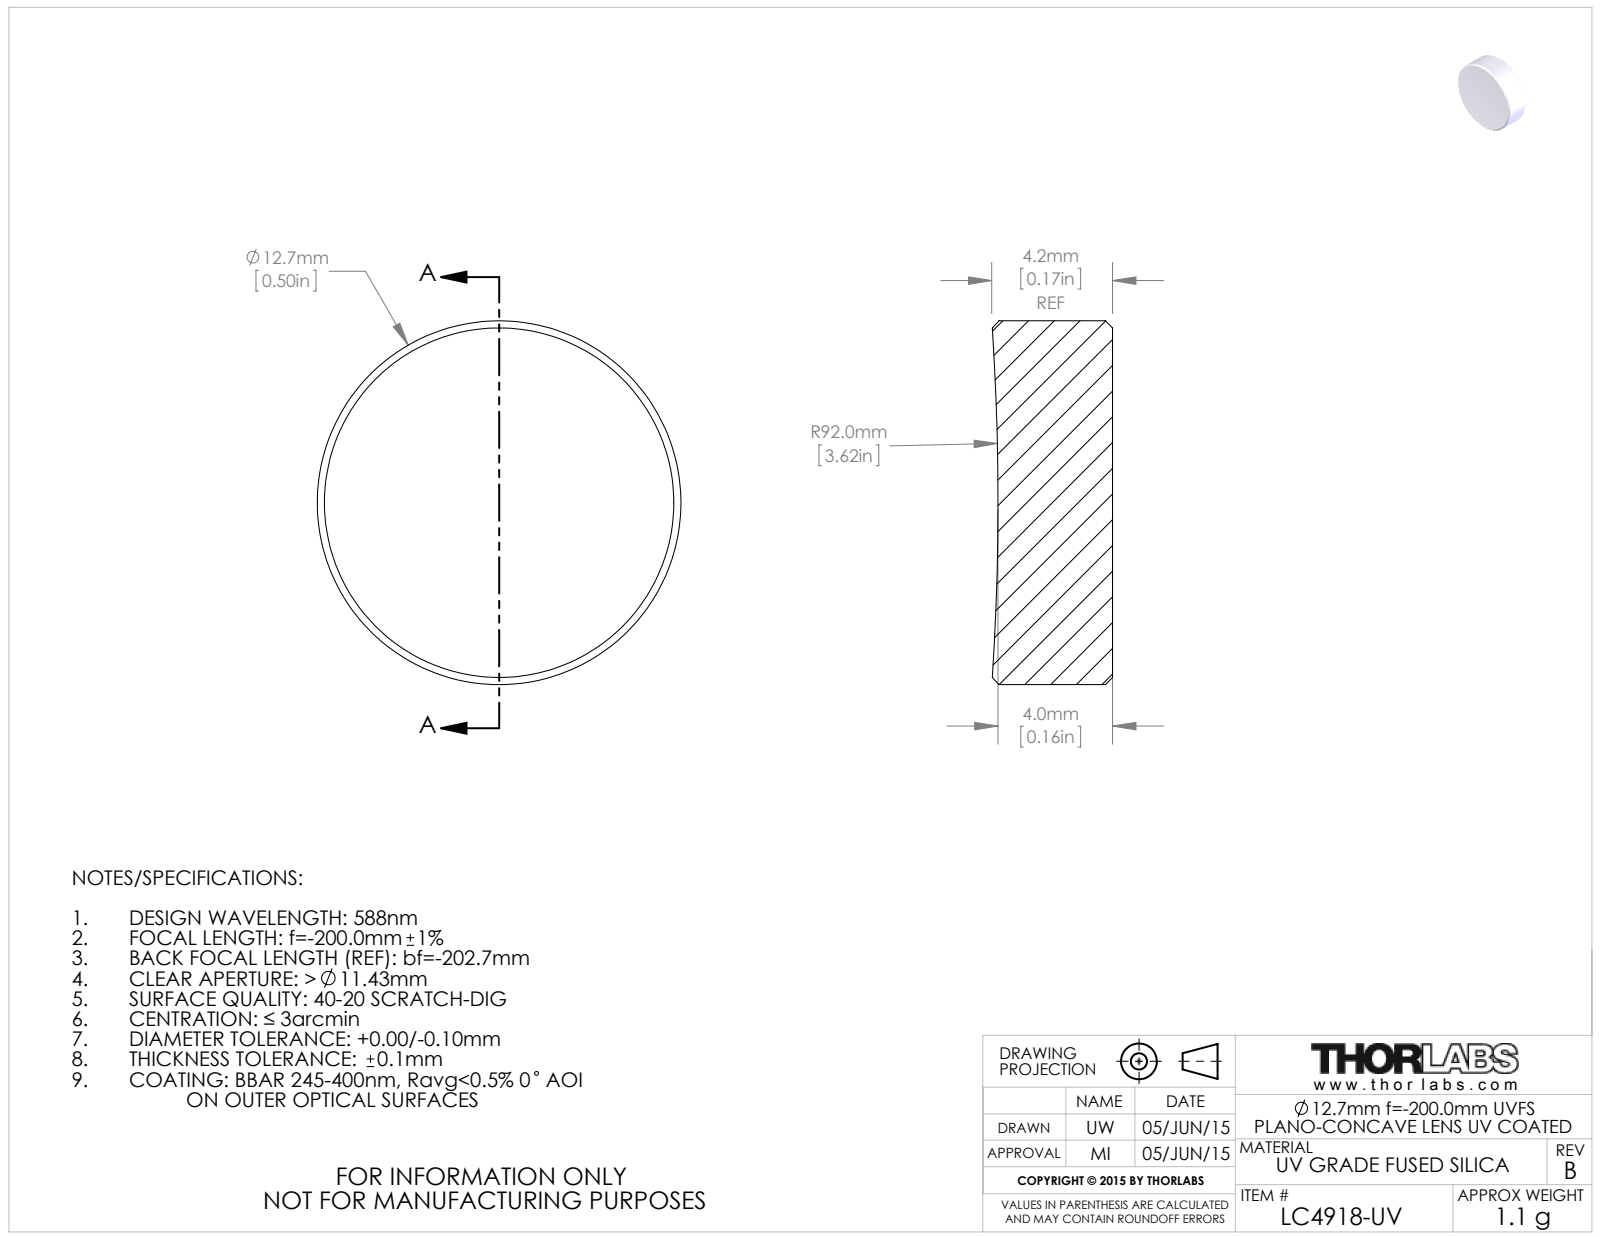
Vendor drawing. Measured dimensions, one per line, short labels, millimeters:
name: 4349-E0W
written by: SolidWorks 2014 (CONFIG_CONTROL_DESIGN)
unit: mm
bodies: 1 solid, 9 faces (1 planar, 2 cylindrical, 6 other)
size: 12.7 × 12.7 × 4.2
volume: 518 mm³; area: 410 mm²
bosses: 1× ⌀12.7
